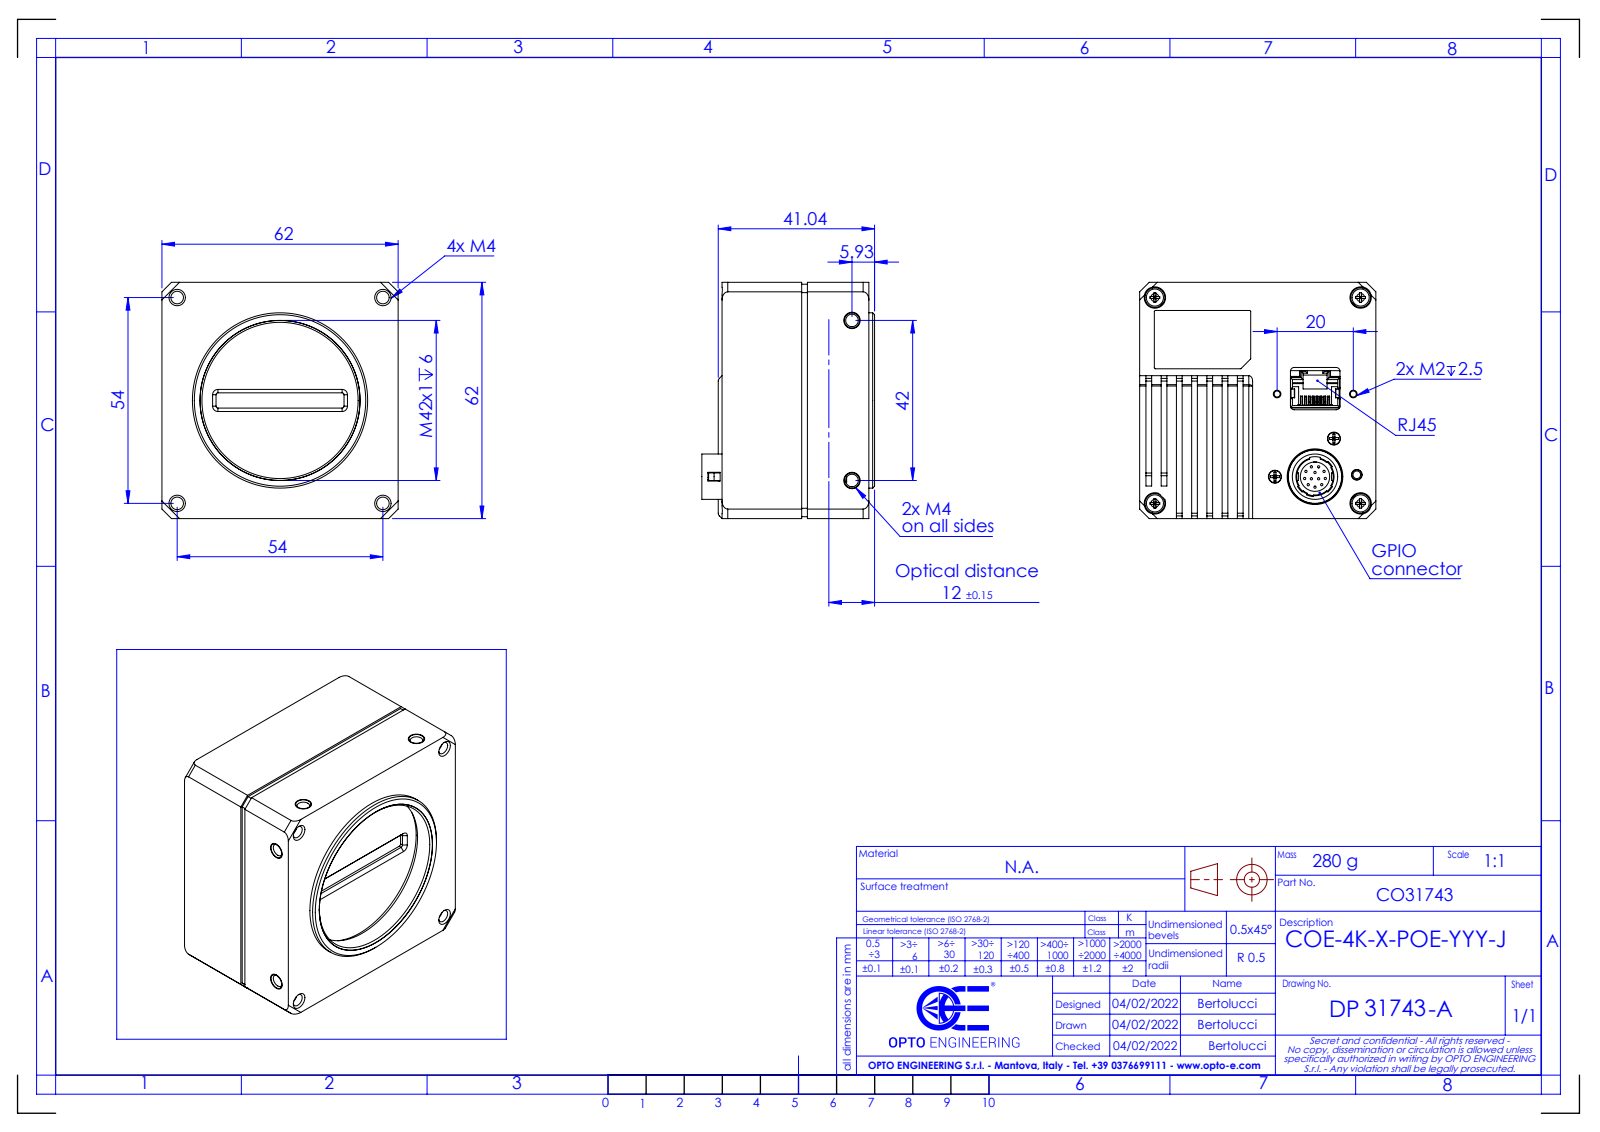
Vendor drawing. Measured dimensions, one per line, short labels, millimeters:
name: DP31743-A_COE-4K-X-POE-YYY-J
written by: SolidWorks 2021 (CONFIG_CONTROL_DESIGN)
unit: mm
bodies: 0 solids, 503 faces (252 planar, 180 cylindrical, 71 other)
size: 62 × 62 × 45.34
holes: 8× ⌀3.3, 4× ⌀5.2, 2× ⌀0.95, 2× ⌀1.6, 1× ⌀2.8, 1× ⌀7.7, 1× ⌀10, 1× ⌀14.2, 1× ⌀41
bosses: 12× ⌀0.6, 4× ⌀4, 2× ⌀3.2, 2× ⌀1.45, 1× ⌀46, 1× ⌀42, 1× ⌀14, 1× ⌀11.9
rounds: 11× R0.3, 9× R1, 8× R1.5, 7× R0.5, 5× R0.25, 2× R0.75, 2× R1.78, 1× R0.12
face distances: 62, 17.63, 2.5, 38.53, 20.9, 1.5, 4, 36.03, 18.4, 4.53
hole spacings: 38.18, 54, 42, 76.37, 5.35, 7.57, 10.15, 10.98
